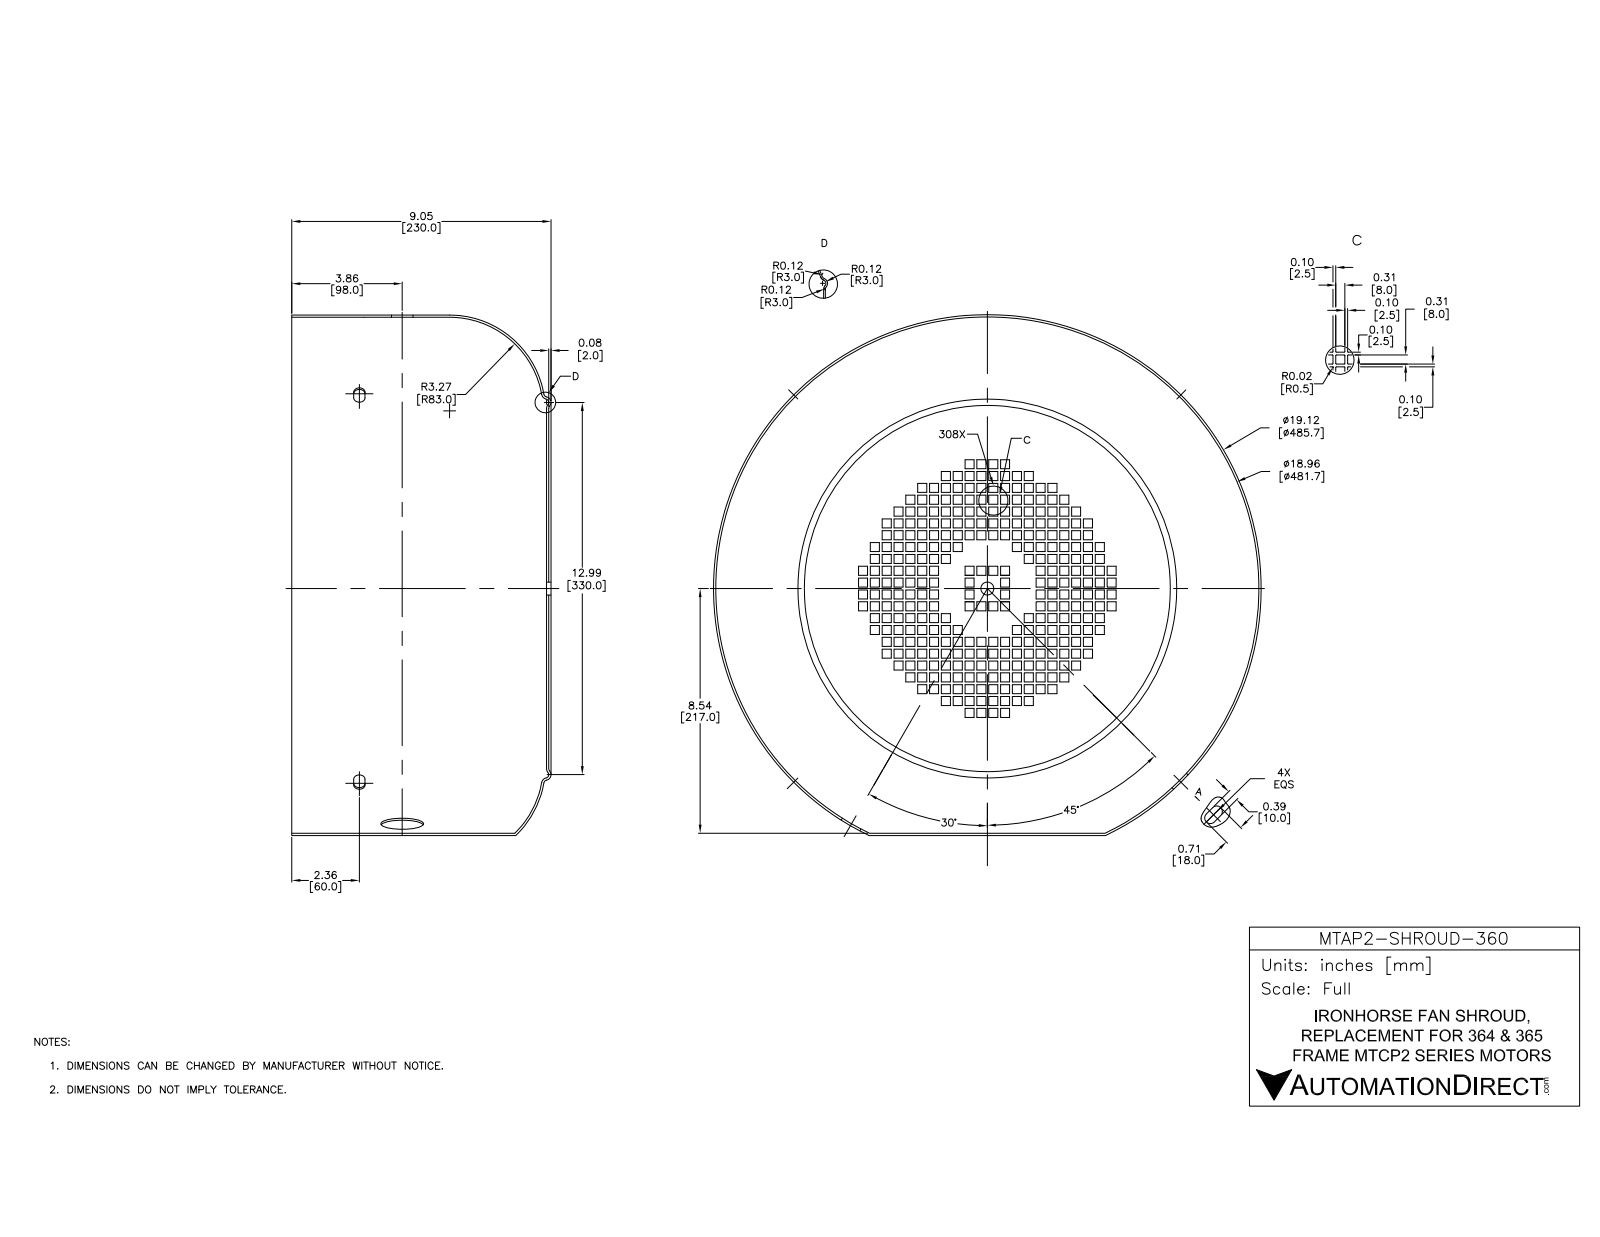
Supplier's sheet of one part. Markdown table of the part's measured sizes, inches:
| quantity | value |
| --- | --- |
| part name | MTAP2-SHROUD-360 |
| STEP written by | SolidWorks 2017 (AUTOMOTIVE_DESIGN) |
| units | inches |
| bodies | 1 solid, 1566 faces (1546 planar, 4 cylindrical, 16 other) |
| overall size | 19.094 × 19.094 × 9.054 |
| volume | 55.78 in³ |
| surface area | 1 468 in² |
| round holes (diameter × count) | 0.453 × 1, 18.937 × 1 |
| round bosses / shafts (diameter × count) | 19.094 × 1 |
| main face-to-face distances | 0.079, 0.039, 8.897, 8.936, 8.976, 0.413, 0.315, 0.827, 1.24, 4.134 |
